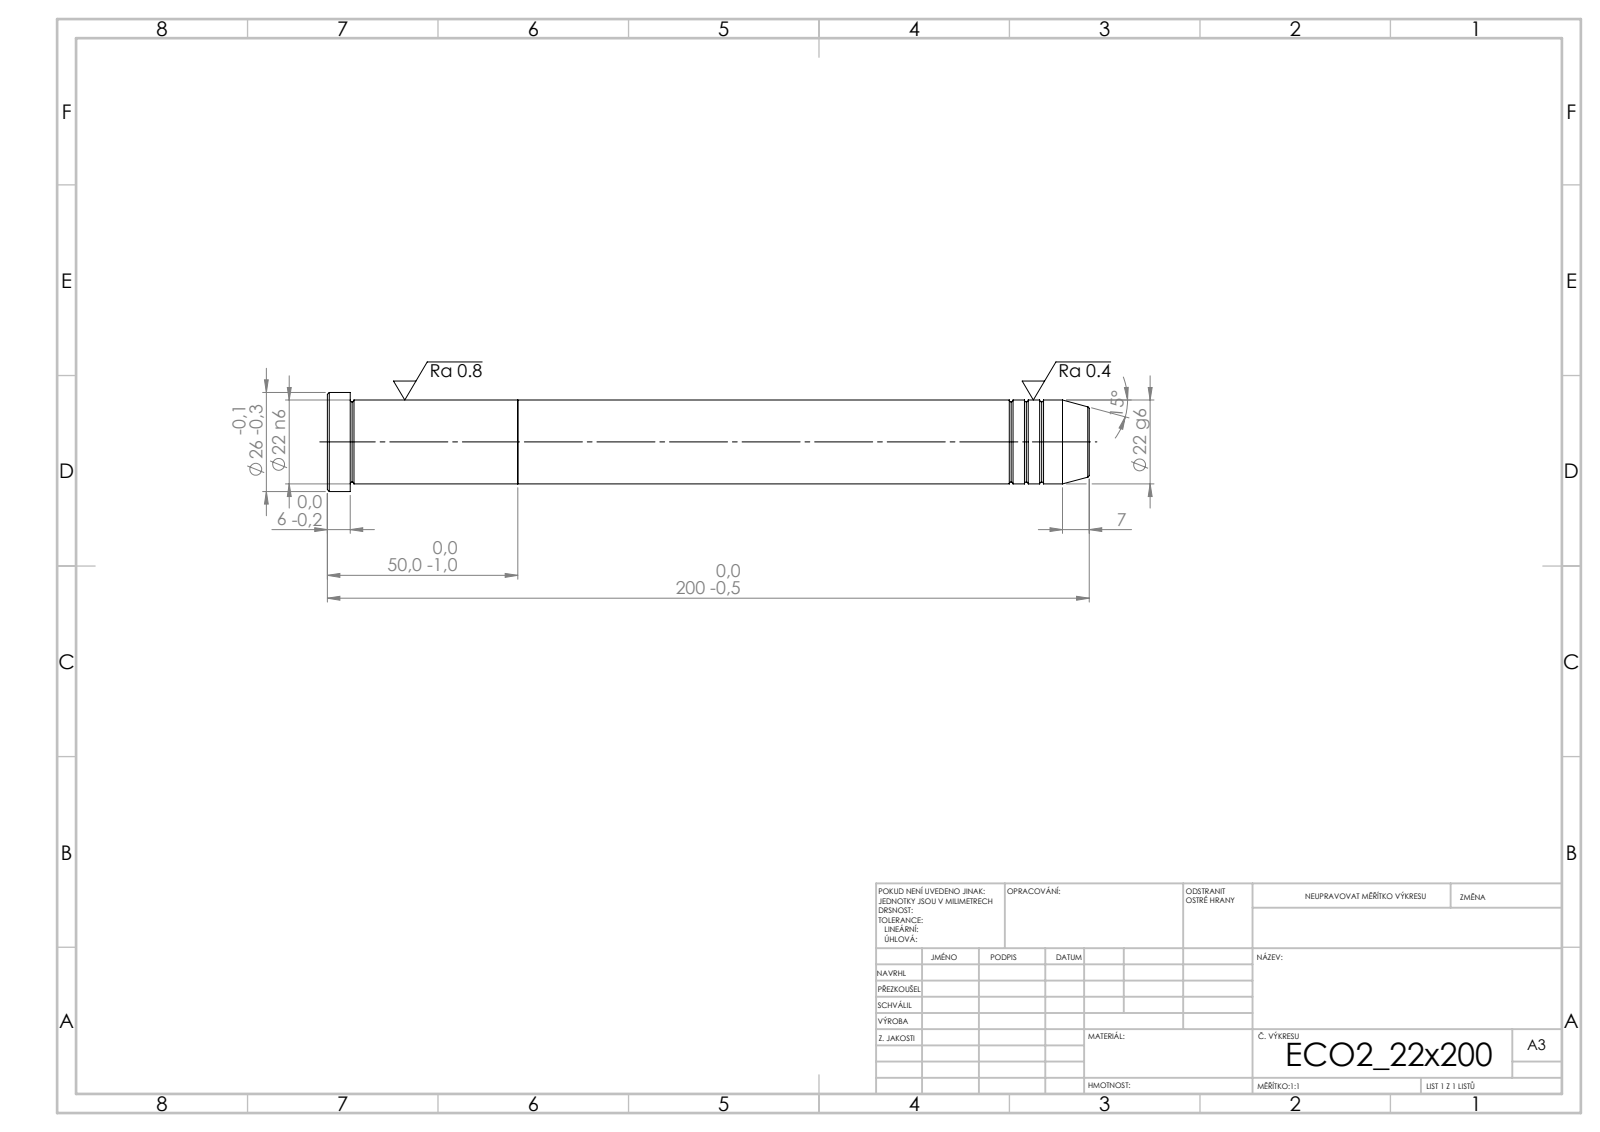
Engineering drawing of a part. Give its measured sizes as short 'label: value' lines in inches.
written by: SolidWorks 2019 (CONFIG_CONTROL_DESIGN)
unit: in
bodies: 2 solids, 39 faces (5 planar, 12 cylindrical, 22 other)
size: 7.874 × 1.024 × 1.024
volume: 4.661 in³; area: 24.32 in²
bosses: 1× ⌀1.024, 1× ⌀0.866
face distances: 1.969, 5.906, 7.874, 7.638, 1.732, 0.236
